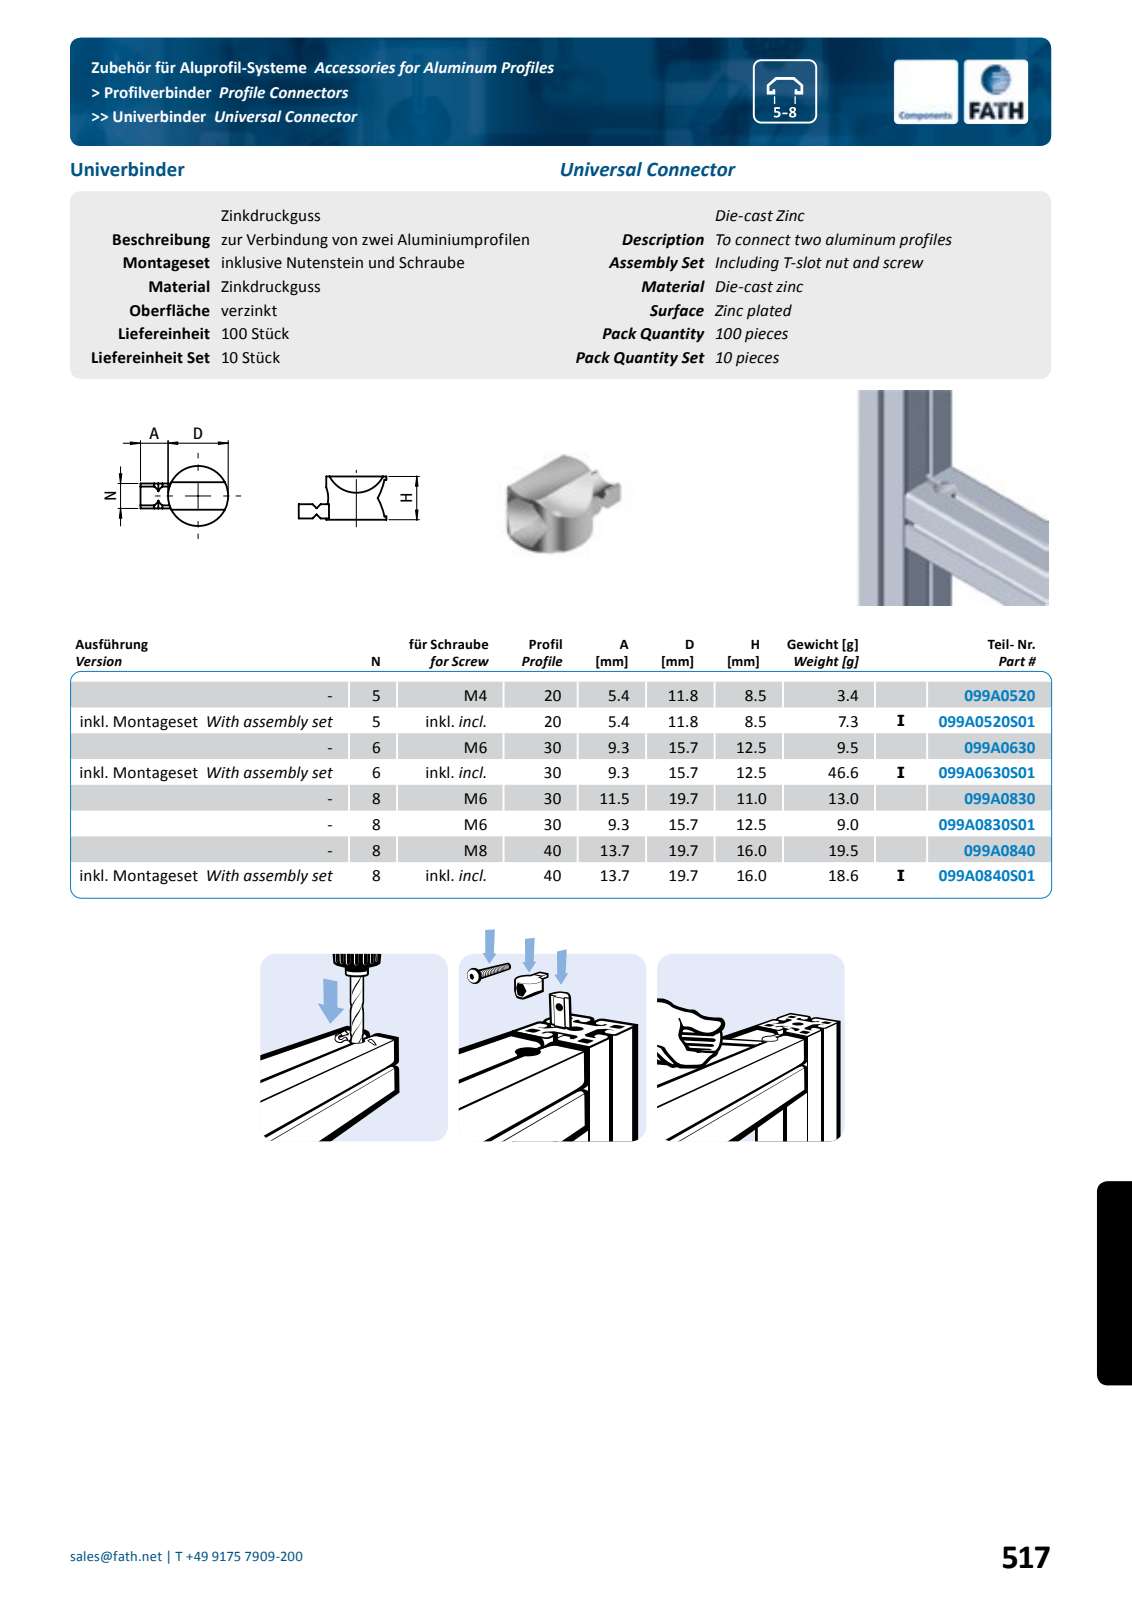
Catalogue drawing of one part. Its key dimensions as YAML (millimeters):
part_name: "fath_099a0840"
step_written_by: "Spatial InterOp 3D (automotive_design)"
units: millimeters
bodies: {solids: 1, faces: 35, planar: 17, cylindrical: 4, other: 14}
overall_size: [33.5, 19.7, 16.2]
volume: 3099
surface_area: 2400
round_holes:
  - {diameter: 8.2, count: 1}
round_bosses_or_shafts:
  - {diameter: 19.7, count: 1}
face_to_face_distances: [16, 3.9, 12.1, 1, 2.9, 15, 7.9, 22.5, 16.2, 15.2]
